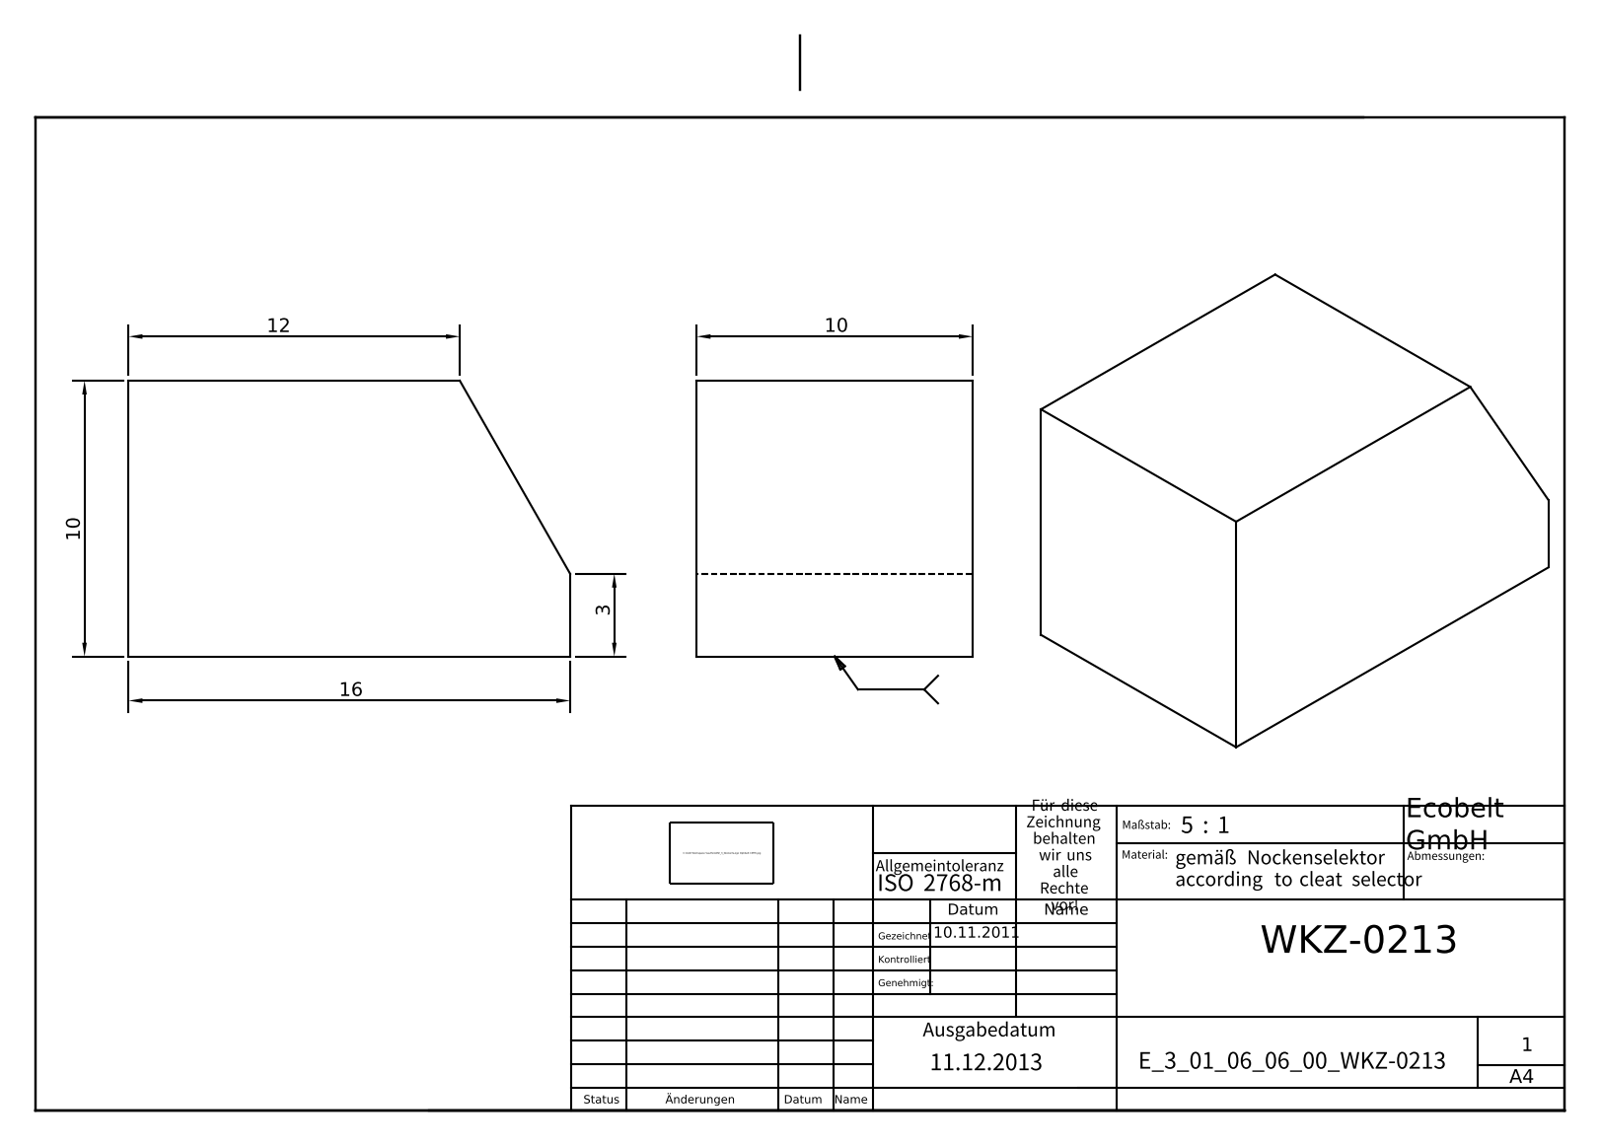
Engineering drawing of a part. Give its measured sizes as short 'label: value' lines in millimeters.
name: E_3_01_06_06_00_WKZ-0213
written by: Autodesk Inventor 2025 (AUTOMOTIVE_DESIGN)
unit: mm
bodies: 1 solid, 7 faces (7 planar, 0 cylindrical, 0 other)
size: 16 × 10 × 10
volume: 1 460 mm³; area: 783 mm²
face distances: 10, 16
